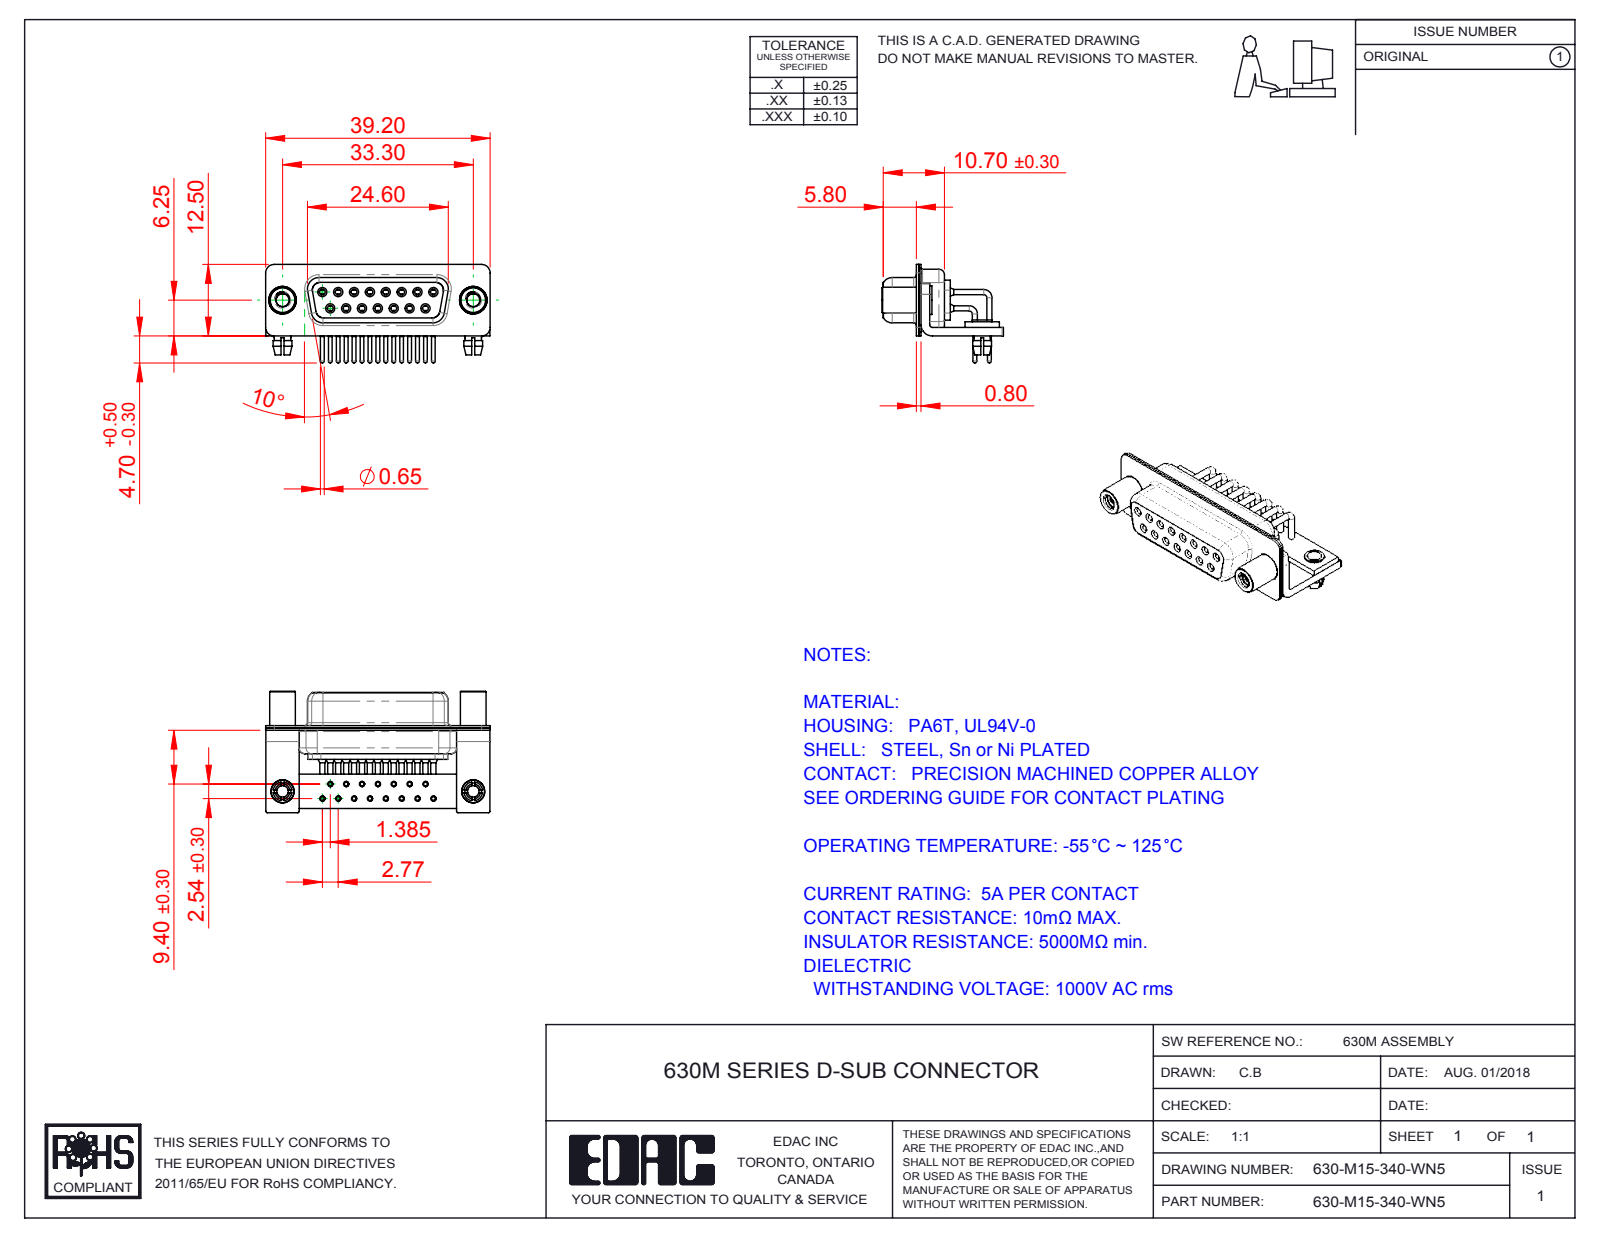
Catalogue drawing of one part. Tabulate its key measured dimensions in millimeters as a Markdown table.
| quantity | value |
| --- | --- |
| part name | 630-M15-340-WN5; 630M Contact Row 2; 630M Stabilizer Bracket; 630M Contact Row 1 (+6 more) |
| STEP written by | SolidWorks 2016 (CONFIG_CONTROL_DESIGN) |
| units | millimeters |
| bodies | 25 solids, 1296 faces (368 planar, 608 cylindrical, 320 other) |
| overall size | 39.2 × 21.2 × 17.2 |
| volume | 3 217 mm³ |
| surface area | 8 278 mm² |
| round holes (diameter × count) | 2 × 17, 0.9 × 15, 1 × 15, 1.1 × 15, 1.7 × 15, 1.8 × 15, 2.26 × 2, 2.5 × 2, 3.2 × 2, 4 × 2, 4.8 × 2 |
| round bosses / shafts (diameter × count) | 0.9 × 27, 1.6 × 15, 1.5 × 15, 0.65 × 15, 5 × 2, 4.9 × 2, 4.5 × 2, 4 × 2 |
| partial cylindrical surfaces (radius × count) | 0.25 × 16, 1.5 × 16, 2 × 13, 1.35 × 8, 1.6 × 8, 0.5 × 5, 0.6 × 4, 0.65 × 4 |
| main face-to-face distances | 0.4, 2.3, 1.9, 0.8, 1.5, 9.35, 1, 1.45, 8.95, 0.85 |
| hole center spacings | 2.77, 5.54, 8.31, 3.16, 4.87, 11.08, 2.89, 7.37 |
